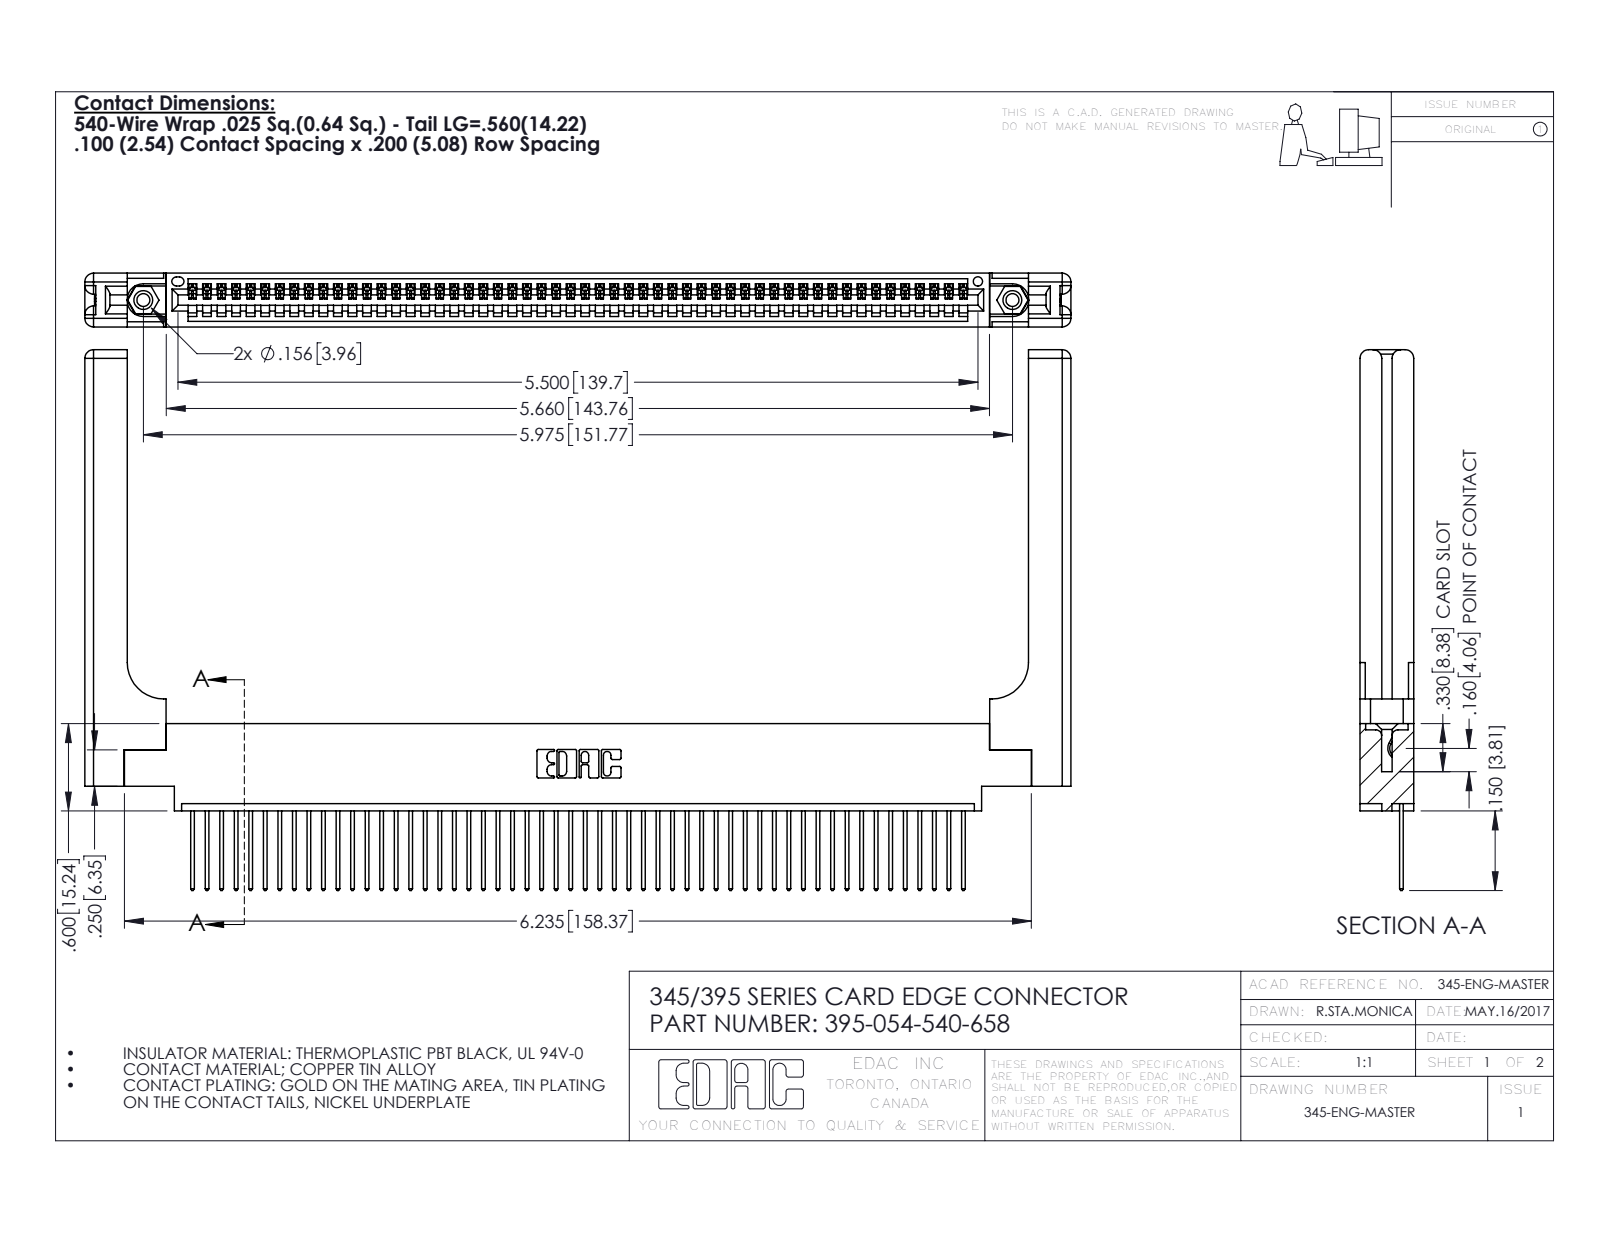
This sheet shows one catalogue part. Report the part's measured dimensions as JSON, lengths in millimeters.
{"part_name": "345 Part_0.170 Offset - 0.156 Dia-TH; 345-292-001_345-293-140; 345-220-058_345-220-058; 395-054-540-658 (+1 more)", "step_written_by": "SolidWorks 2016 (CONFIG_CONTROL_DESIGN)", "units": "millimeters", "bodies": {"solids": 59, "faces": 3518, "planar": 2392, "cylindrical": 1066, "other": 60}, "overall_size": [172.2, 94.4, 9.4], "volume_mm3": 24920, "surface_area_mm2": 27930, "round_holes": [[2.3, 2], [3.2, 2], [4, 2], [1.6, 1]], "round_bosses_or_shafts": [[3.9, 2]], "partial_cylinders_radius": [[0.2, 108], [0.3, 108], [0.3, 22], [1.5, 16], [0.2, 6], [0.8, 6], [0.7, 3], [0.8, 2]], "face_to_face_distances": [1.8, 9.4, 7.6, 2.5, 6.9, 0.6, 5.1, 5.7, 3.8, 3.8], "hole_center_spacings": [6.9, 145.8, 151.8]}
